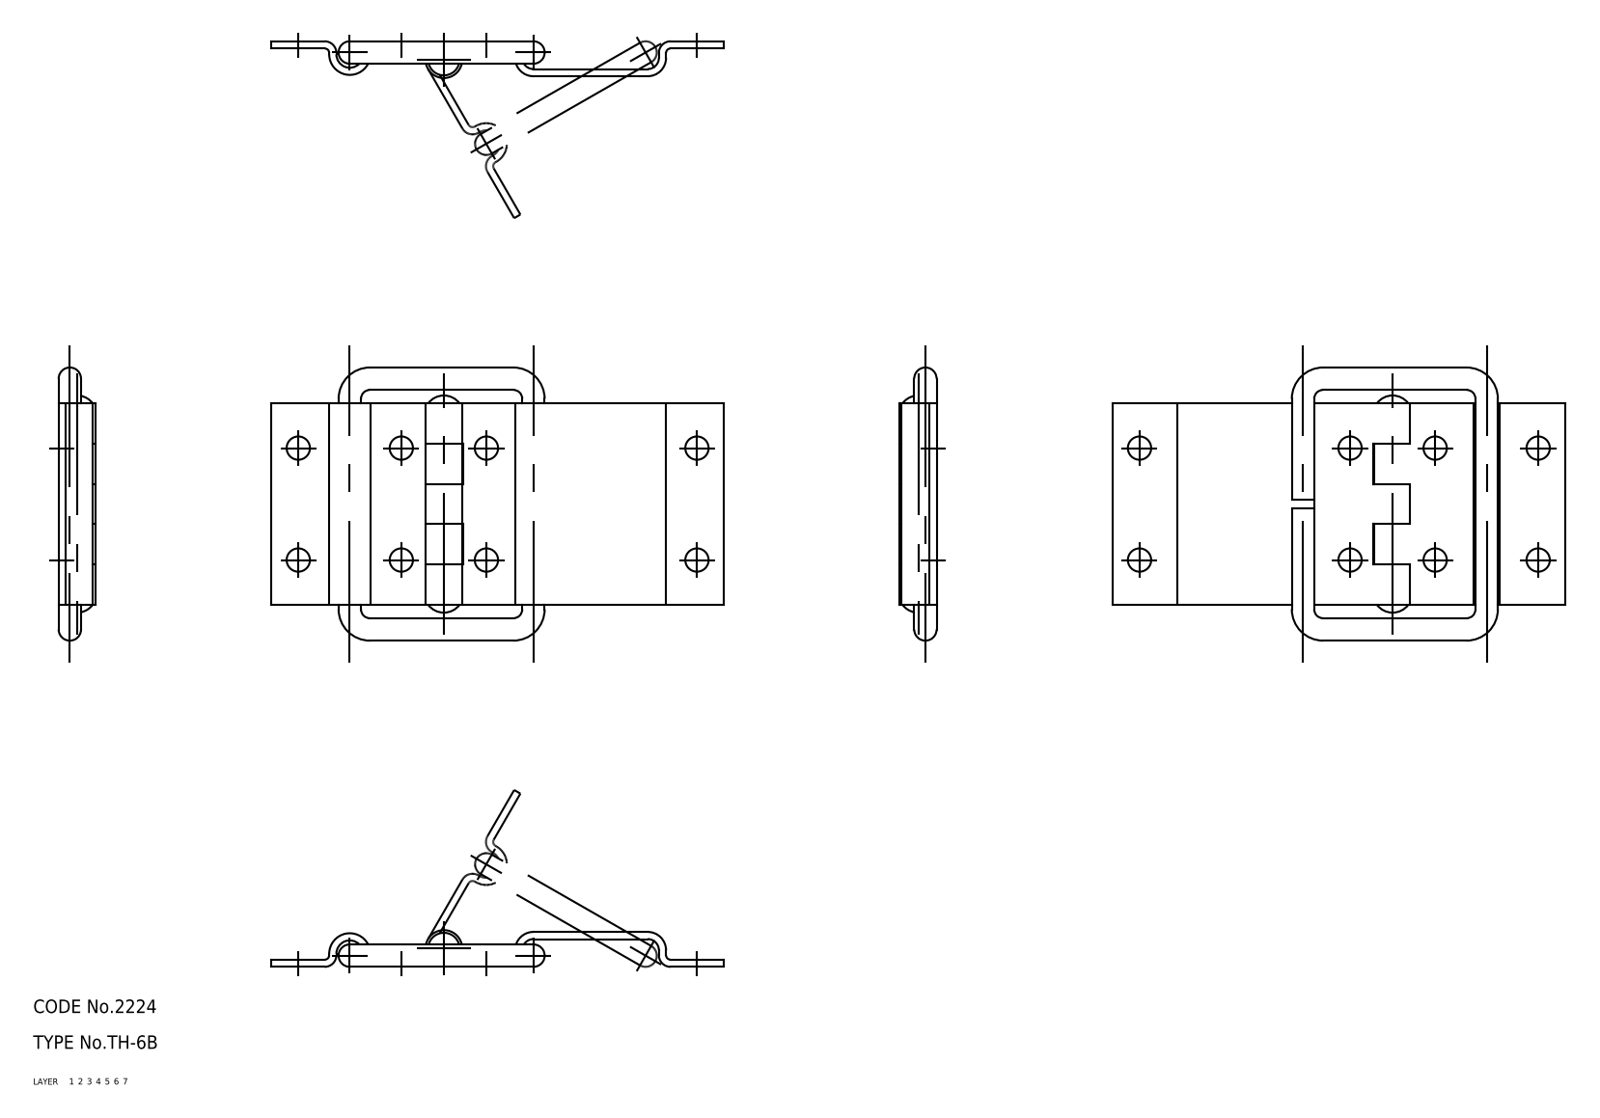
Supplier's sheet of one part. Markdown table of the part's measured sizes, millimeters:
| quantity | value |
| --- | --- |
| part name | hinge piece_A; hinge piece_B; shaft; stopper (+1 more) |
| STEP written by | SolidWorks 2015 (AUTOMOTIVE_DESIGN) |
| units | millimeters |
| bodies | 4 solids, 128 faces (46 planar, 70 cylindrical, 12 other) |
| overall size | 101 × 61 × 8.2 |
| volume | 13 624 mm³ |
| surface area | 16 278 mm² |
| round holes (diameter × count) | 5.2 × 8, 5 × 1 |
| round bosses / shafts (diameter × count) | 5 × 4, 8.2 × 1 |
| partial cylindrical surfaces (radius × count) | 1 × 4, 2.6 × 4, 2.5 × 2, 4.1 × 2, 3 × 1, 4.6 × 1 |
| main face-to-face distances | 1.6, 6.2, 7.8, 4.6, 9, 18, 45, 27, 36, 14.5 |
| hole center spacings | 25, 19, 23, 31.4, 33.97, 42, 47, 48.88 |
